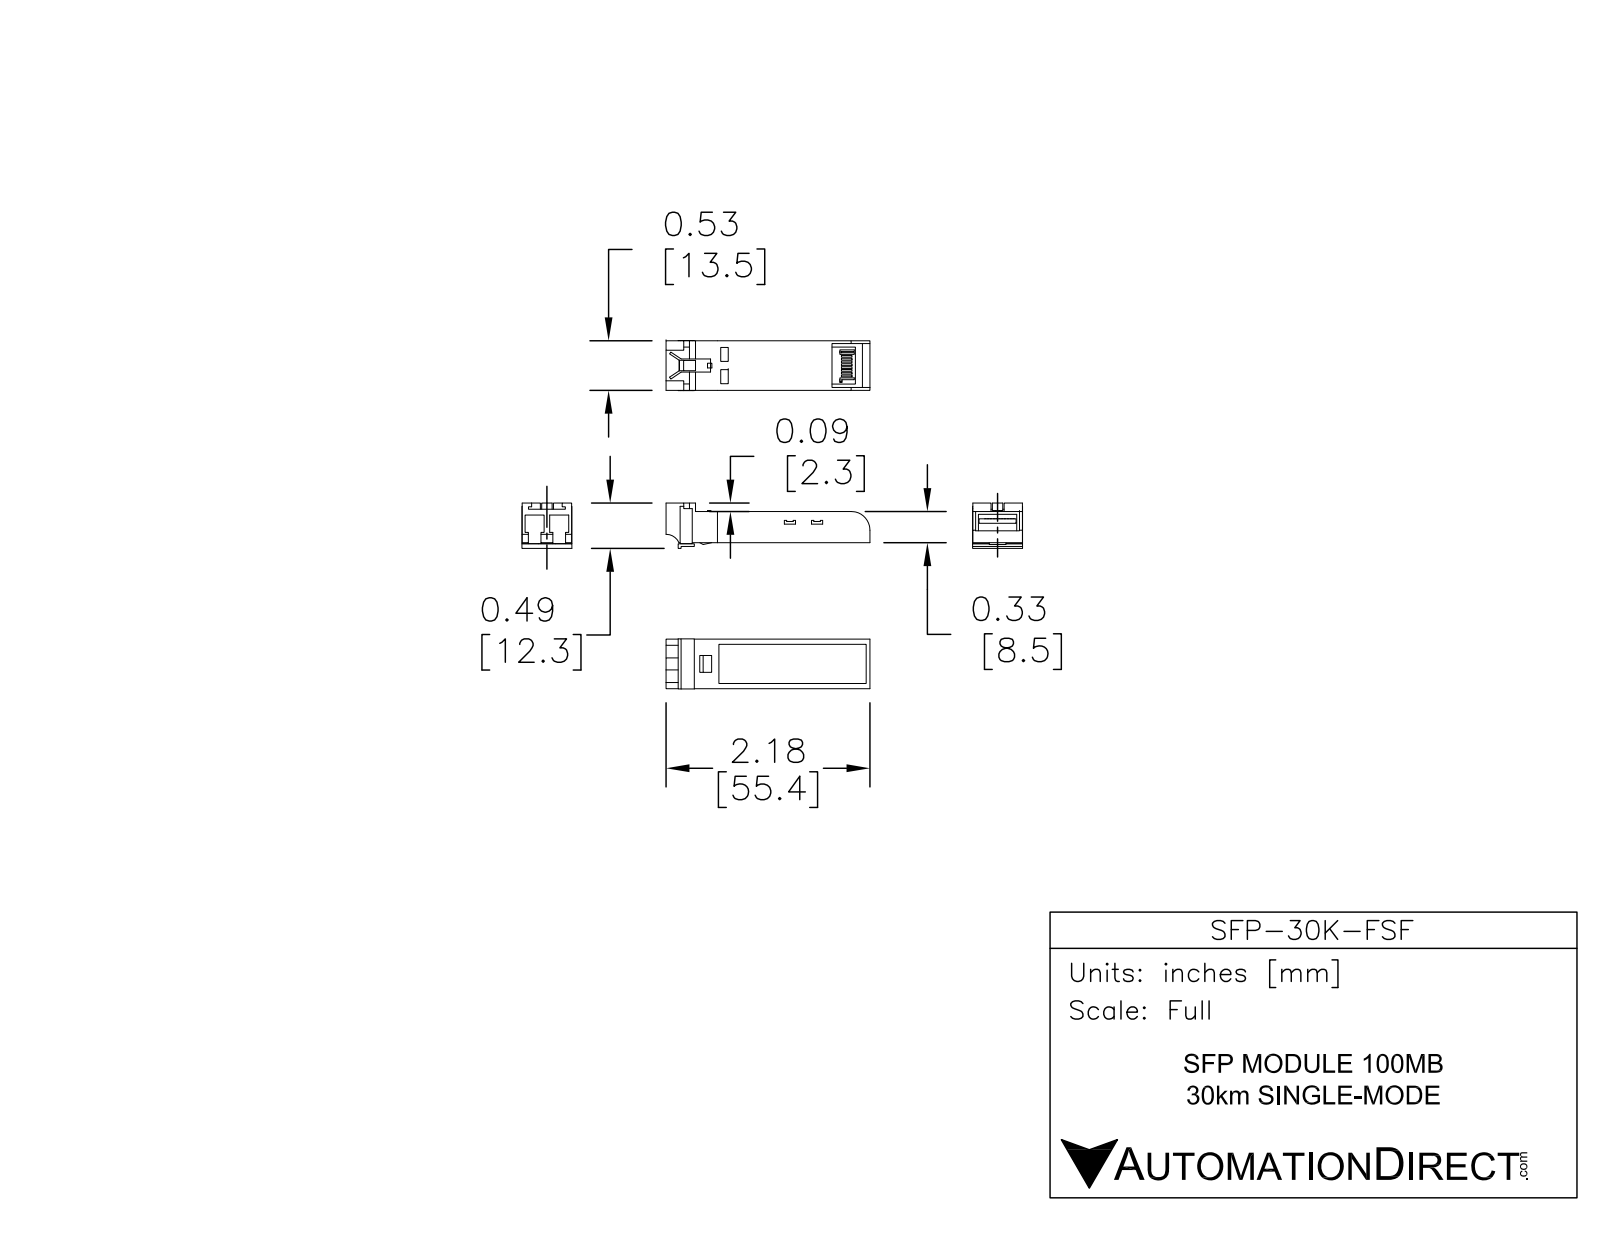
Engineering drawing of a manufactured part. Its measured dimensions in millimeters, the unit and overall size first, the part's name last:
Units: millimetres
Overall size (bounding box): 55.4 × 13.6 × 12.3
Partial cylindrical surfaces — rounded edges, fillets, slot ends (radius × count): R3.8 ×1, R5.1 ×1
Main face-to-face distances: 13.5, 8.5, 0.8, 8.5, 12.7, 7.5, 0.9, 5.3, 6.5, 5.3
Volume: 5 060 mm³ · Surface area: 3 901 mm²
Bodies: 2 solids, 227 faces (222 planar, 5 cylindrical, 0 other)
Part name (STEP PRODUCT): SFP-30K-FSF
STEP written by: SolidWorks 2011 (AUTOMOTIVE_DESIGN)
